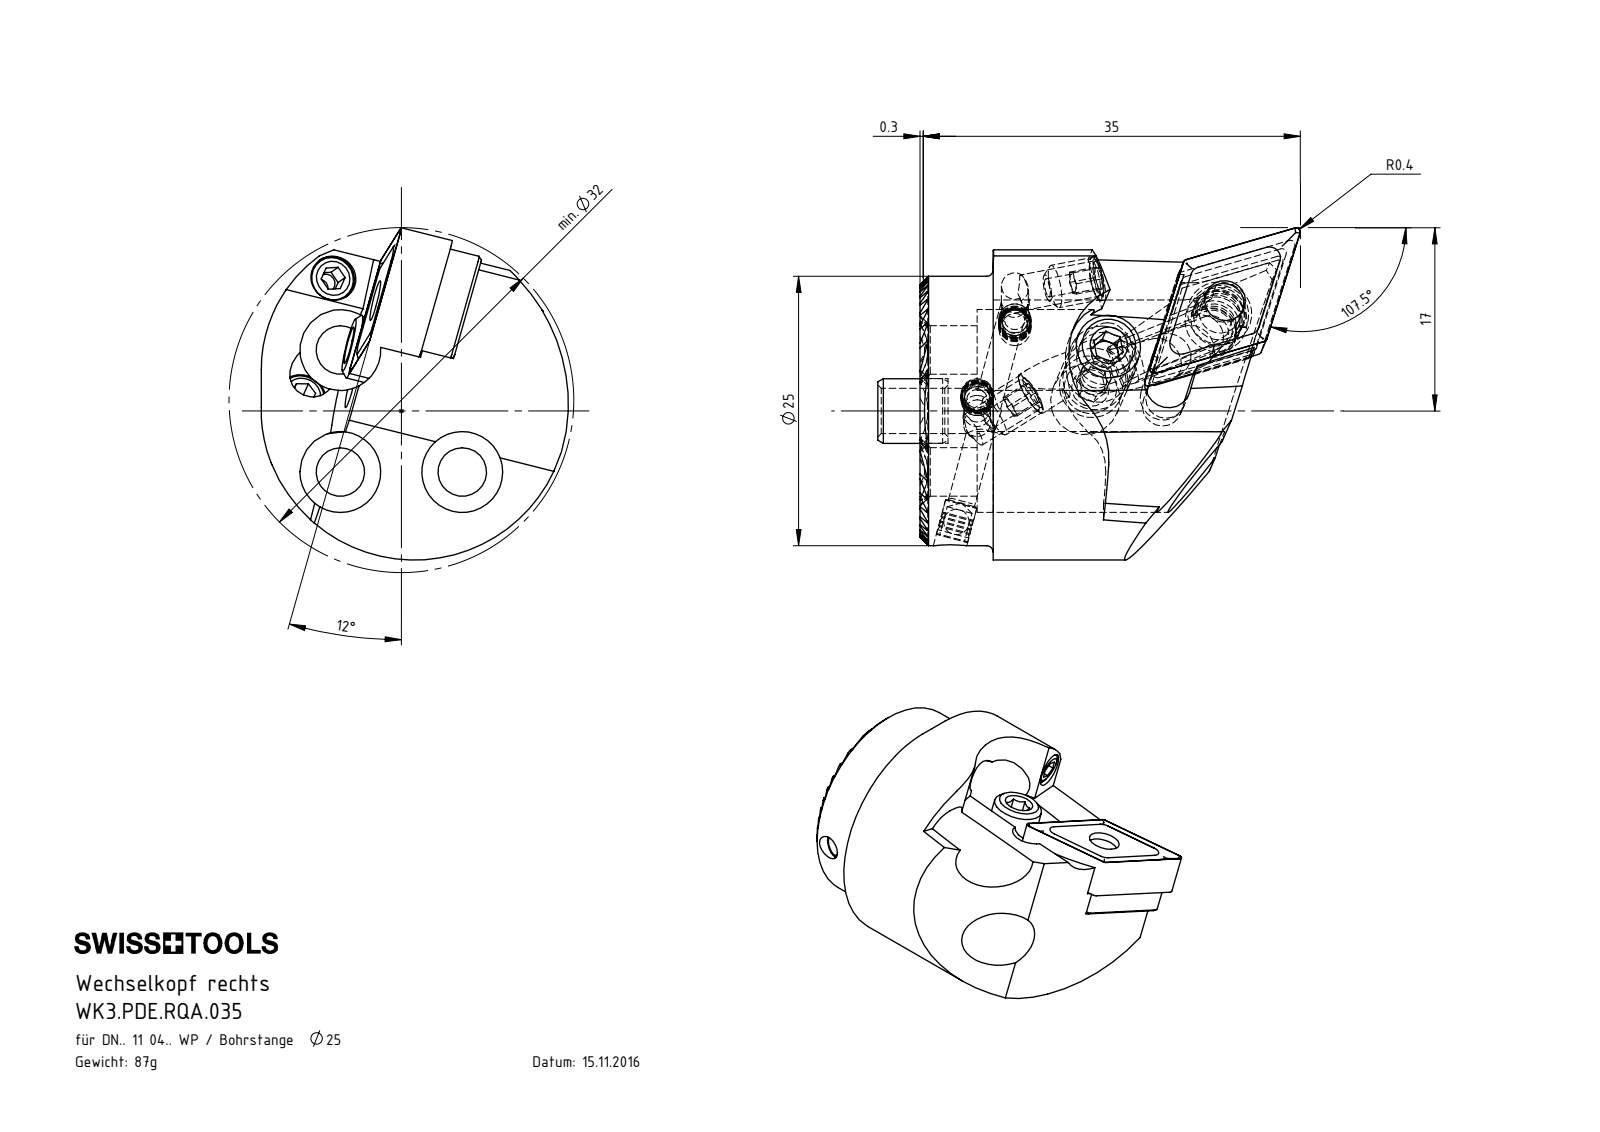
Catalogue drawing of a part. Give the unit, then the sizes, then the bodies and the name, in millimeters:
Units: millimetres
Overall size (bounding box): 39.21 × 30.83 × 28.51
Round holes (diameter × count): ⌀2.38 ×3, ⌀2.5 ×3, ⌀3 ×3, ⌀4.2 ×3, ⌀4.5 ×3, ⌀7.5 ×3, ⌀1.7 ×2, ⌀3.3 ×2, ⌀3.81 ×1, ⌀4.8 ×1, ⌀5 ×1, ⌀6 ×1
Round bosses / shafts (diameter × count): ⌀3 ×3, ⌀4 ×2, ⌀25 ×1, ⌀6 ×1, ⌀5.9 ×1, ⌀2.87 ×1
Partial cylindrical surfaces — rounded edges, fillets, slot ends (radius × count): R0.12 ×20, R0.4 ×8, R2.1 ×5, R7 ×2, R13 ×2, R1.83 ×1, R1.85 ×1, R2.25 ×1
Main face-to-face distances: 4.33, 1.08, 3.25, 5.41, 8.66, 7.58, 2.16, 2.17, 9.74, 6.5
Hole centre spacings: 8, 11.32, 11.78, 11.79, 16.01
Volume: 11 495 mm³ · Surface area: 8 422 mm²
Bodies: 15 solids, 456 faces (236 planar, 104 cylindrical, 116 other)
Part name (STEP PRODUCT): WDE-ER4.101.017_A; WDE-ER2.101.003_A; WDE-ER3.101.000_A; WK3-PDE.RQA.035_A (+6 more)
STEP written by: SolidWorks 2017 (AUTOMOTIVE_DESIGN)
